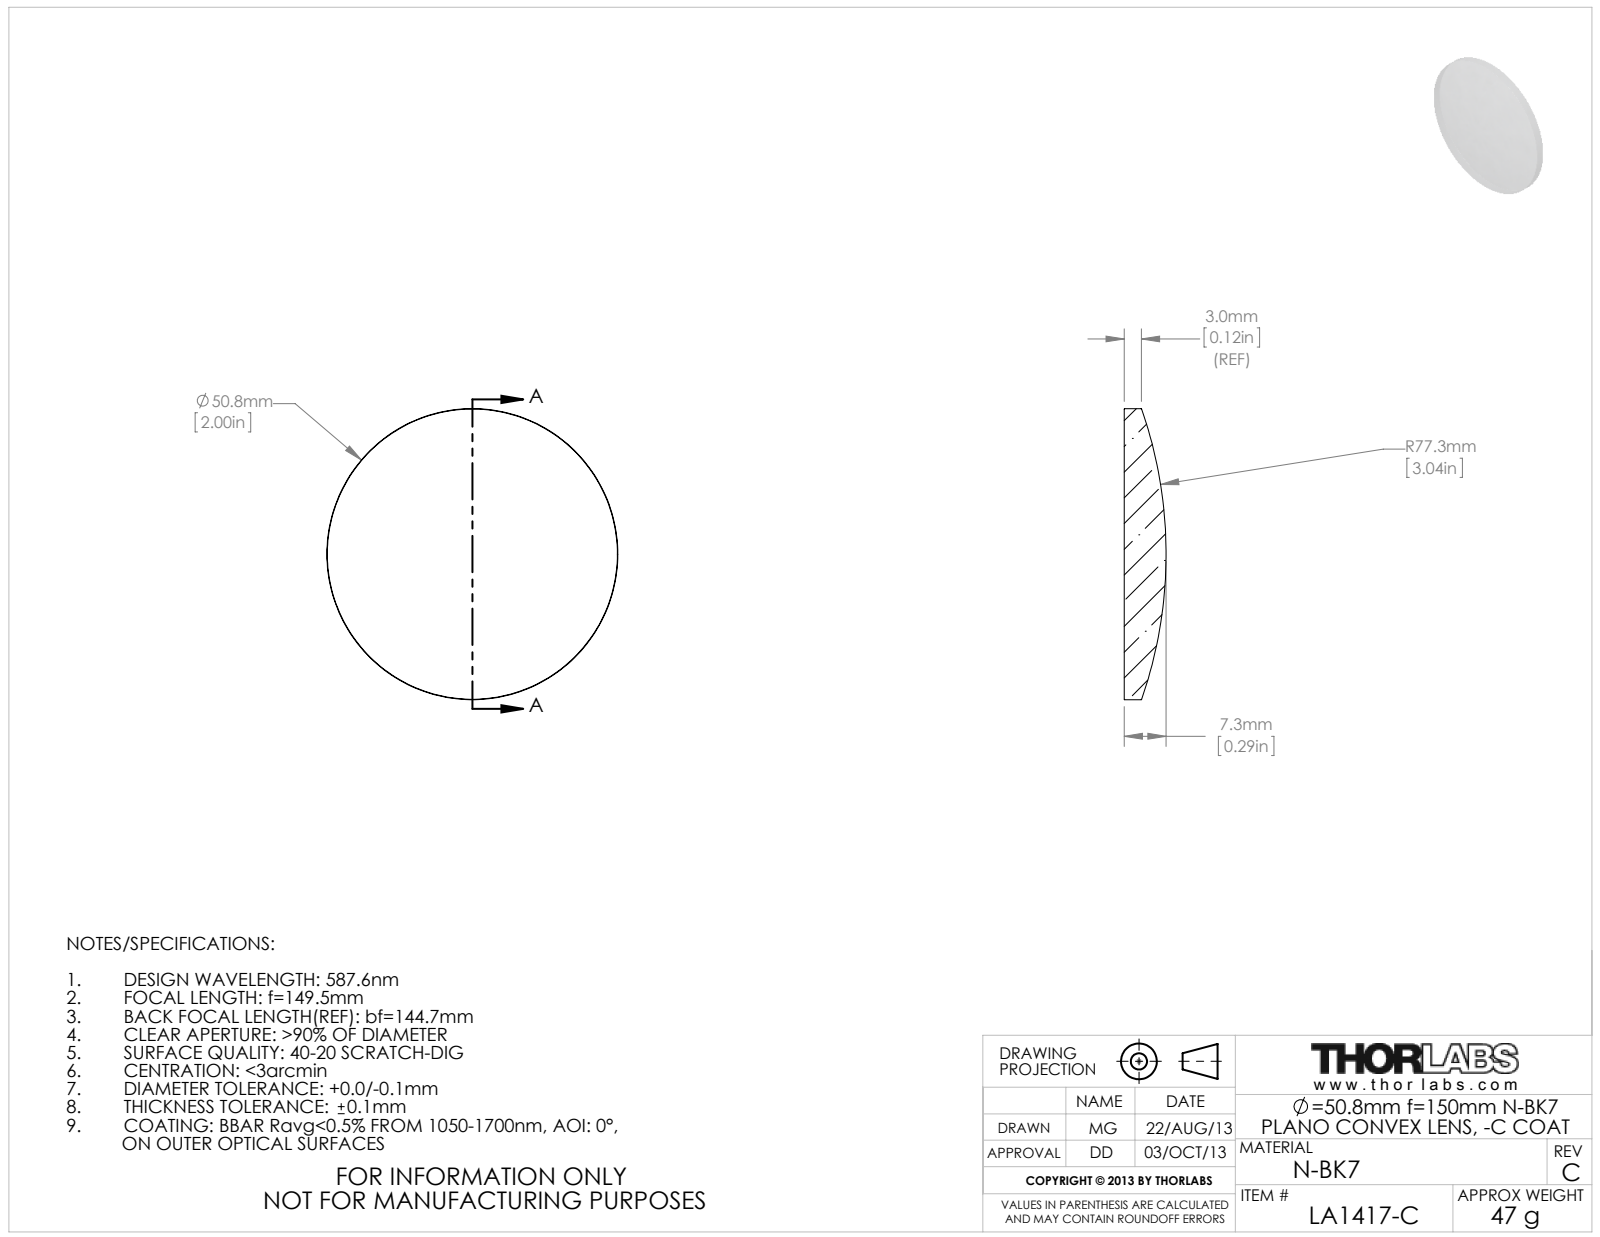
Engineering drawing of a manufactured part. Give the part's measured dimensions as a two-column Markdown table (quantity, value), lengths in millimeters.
| quantity | value |
| --- | --- |
| part name | 4604-E0W |
| STEP written by | SolidWorks 2009 (AUTOMOTIVE_DESIGN) |
| units | millimeters |
| bodies | 0 solids, 5 faces (1 planar, 2 cylindrical, 2 other) |
| overall size | 50.8 × 50.8 × 7.29 |
| round bosses / shafts (diameter × count) | 50.8 × 1 |
